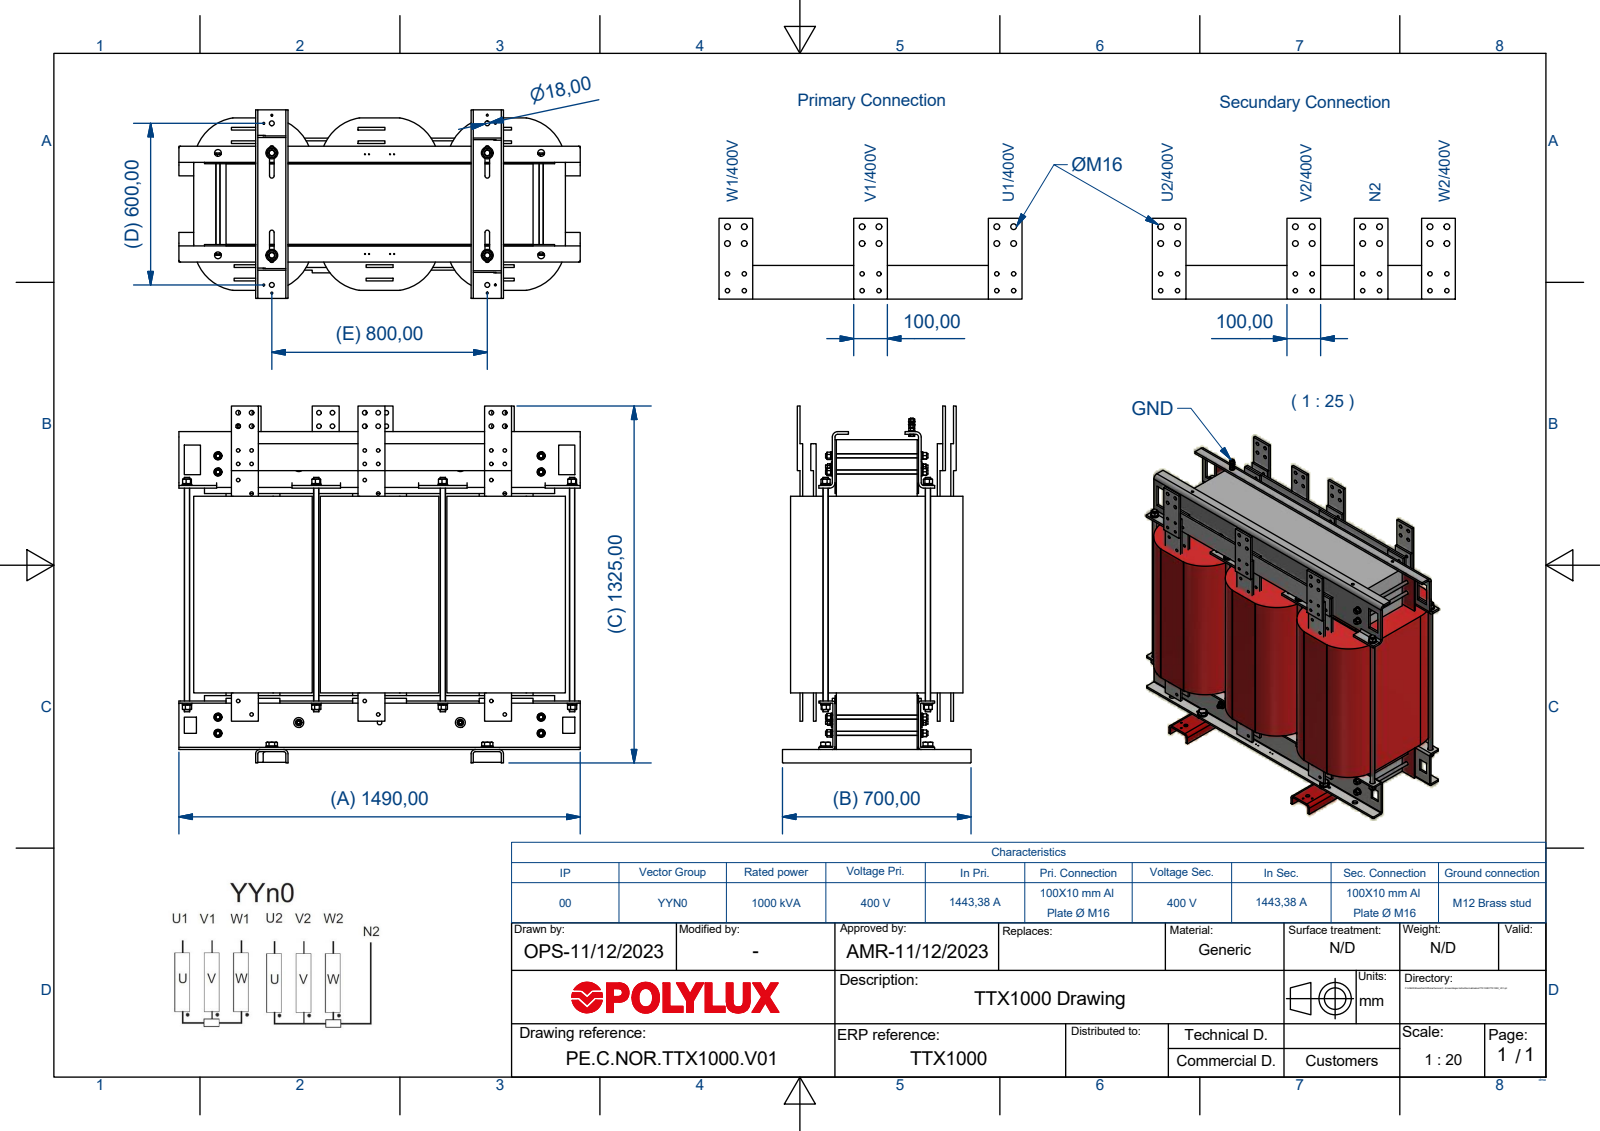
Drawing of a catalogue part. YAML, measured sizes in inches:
part_name: "TTX1000_V01"
step_written_by: "Autodesk Inventor 2018 (AUTOMOTIVE_DESIGN)"
units: inches
bodies: {solids: 202, faces: 2213, planar: 1235, cylindrical: 674, other: 304}
overall_size: [58.661, 52.165, 27.559]
volume: 45700
surface_area: 37560
round_holes:
  - {diameter: 0.512, count: 58}
  - {diameter: 0.669, count: 50}
  - {diameter: 0.984, count: 16}
  - {diameter: 0.433, count: 14}
  - {diameter: 0.866, count: 12}
  - {diameter: 0.591, count: 10}
  - {diameter: 0.138, count: 8}
  - {diameter: 0.276, count: 8}
  - {diameter: 0.545, count: 8}
  - {diameter: 0.681, count: 8}
  - {diameter: 0.827, count: 8}
  - {diameter: 0.835, count: 8}
round_bosses_or_shafts:
  - {diameter: 1.457, count: 12}
  - {diameter: 0.945, count: 9}
  - {diameter: 1.323, count: 8}
  - {diameter: 1.181, count: 8}
  - {diameter: 1.079, count: 8}
  - {diameter: 0.787, count: 8}
  - {diameter: 0.63, count: 8}
  - {diameter: 0.831, count: 5}
partial_cylinders:
  - {radius: 0.591, count: 12}
  - {radius: 6.778, count: 12}
  - {radius: 0.335, count: 8}
  - {radius: 0.394, count: 8}
  - {radius: 0.315, count: 6}
  - {radius: 0.079, count: 4}
  - {radius: 0.236, count: 4}
  - {radius: 0.63, count: 4}
face_to_face_distances: [18.504, 0.197, 12.008, 0.394, 4.724, 11.811, 37.008, 12.598, 17.323, 7.874]
hole_center_spacings: [2.756, 23.622, 1.181, 2.362, 3.63, 38.189, 38.288, 44.488]
